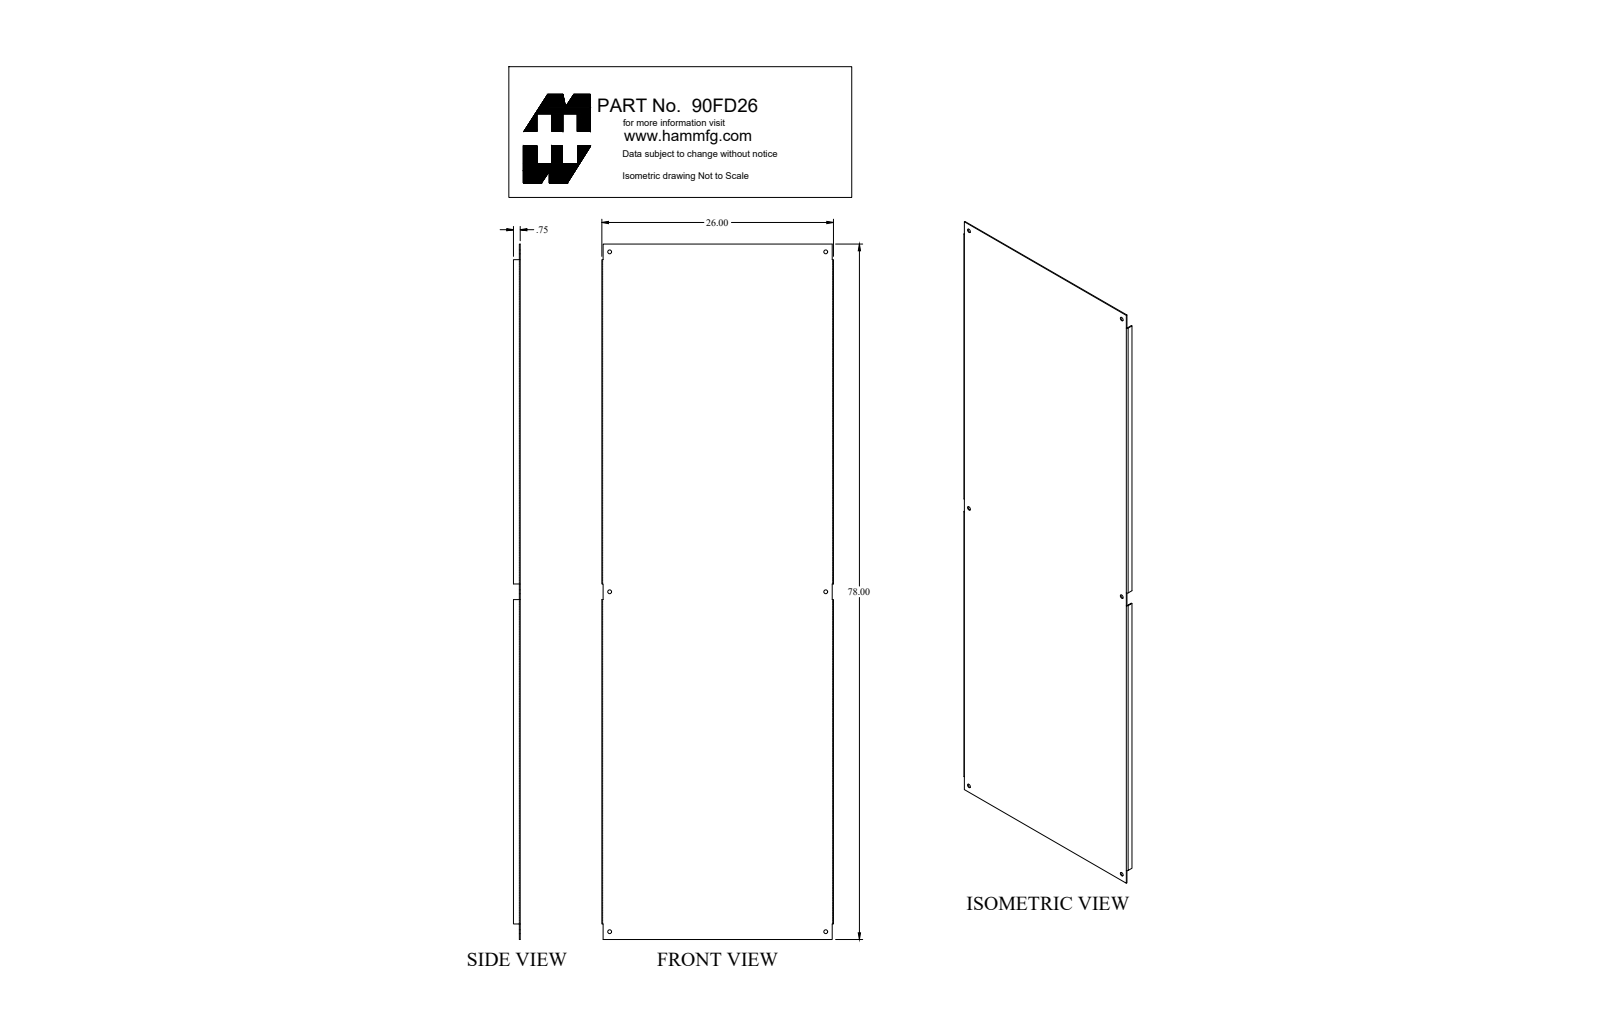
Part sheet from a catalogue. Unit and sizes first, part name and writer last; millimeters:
Units: millimetres
Overall size (bounding box): 1981.2 × 660.4 × 19.1
Round holes (diameter × count): ⌀11.1 ×6
Partial cylindrical surfaces — rounded edges, fillets, slot ends (radius × count): R1.2 ×2, R3.6 ×2
Main face-to-face distances: 2.4, 658, 660.4, 655.6, 19.1, 16.6, 1981.2, 3.6, 656.8, 1.2
Hole centre spacings: 968.4, 1147.7, 616, 1936.8, 2032.3
Volume: 3 292 000 mm³ · Surface area: 2 743 000 mm²
Bodies: 1 solid, 50 faces (30 planar, 20 cylindrical, 0 other)
Part name (STEP PRODUCT): 90FD26_Default
STEP written by: SolidWorks 2018 (CONFIG_CONTROL_DESIGN)
